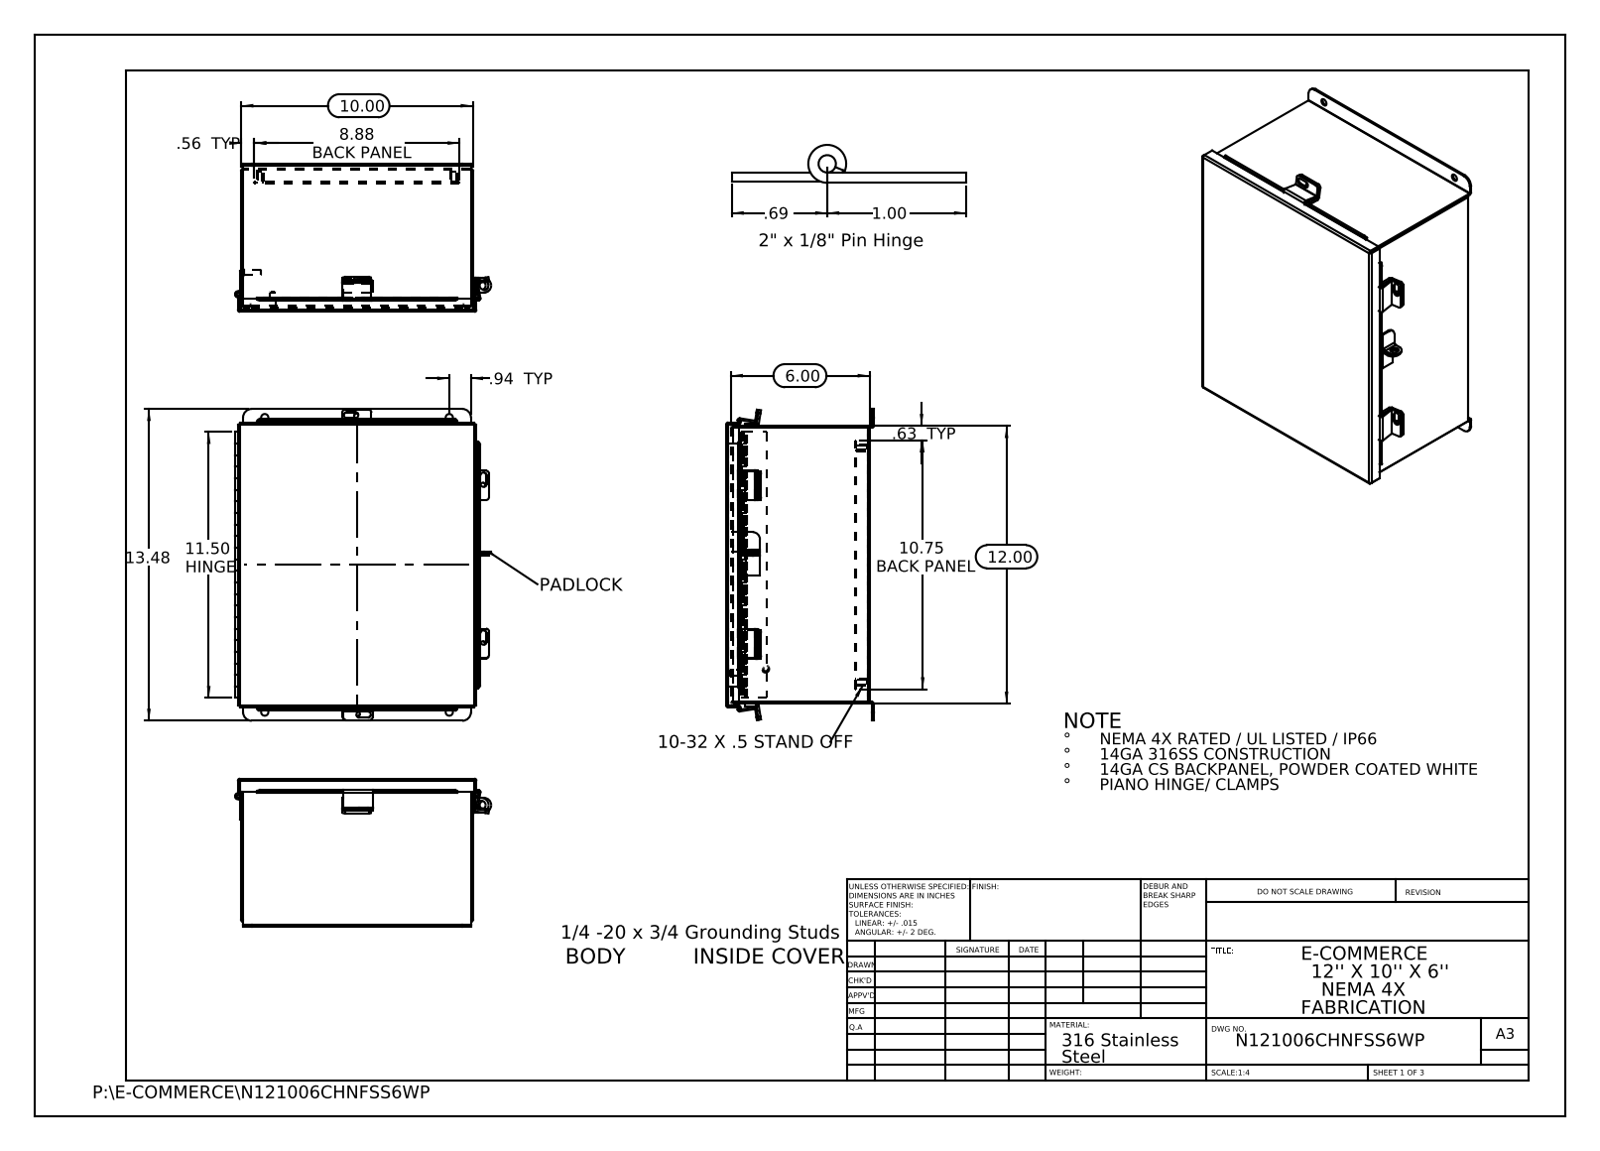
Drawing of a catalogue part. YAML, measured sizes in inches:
part_name: "N121006CHNFSS6WP JIC Bottom; N121006CHNFSS6WP; N121006CHNFSS6WP _JIC Hinge; N121006CHNFSS6WP JIC Clamp Bracket (+8 more)"
step_written_by: "SolidWorks 2013 (CONFIG_CONTROL_DESIGN)"
units: inches
bodies: {solids: 23, faces: 702, planar: 435, cylindrical: 247, other: 20}
overall_size: [13.476, 11.072, 6.39]
volume: 51.8
surface_area: 1415
round_holes:
  - {diameter: 0.25, count: 8}
  - {diameter: 0.187, count: 4}
  - {diameter: 0.312, count: 4}
  - {diameter: 0.125, count: 1}
  - {diameter: 0.125, count: 1}
  - {diameter: 0.373, count: 1}
  - {diameter: 0.375, count: 1}
round_bosses_or_shafts:
  - {diameter: 0.313, count: 4}
  - {diameter: 0.315, count: 2}
  - {diameter: 0.236, count: 2}
  - {diameter: 0.273, count: 1}
  - {diameter: 0.25, count: 1}
partial_cylinders:
  - {radius: 0.125, count: 14}
  - {radius: 0.013, count: 13}
  - {radius: 0.009, count: 12}
  - {radius: 0.088, count: 12}
  - {radius: 0.133, count: 8}
  - {radius: 0.083, count: 6}
  - {radius: 0.1, count: 6}
  - {radius: 0.375, count: 4}
face_to_face_distances: [0.075, 6.128, 9.925, 11.925, 6.053, 6.203, 0.074, 0.575, 0.5, 5.553]
hole_center_spacings: [1.315, 8.278, 11.428, 14.05, 7.976, 8.375, 10.126, 12.726]
